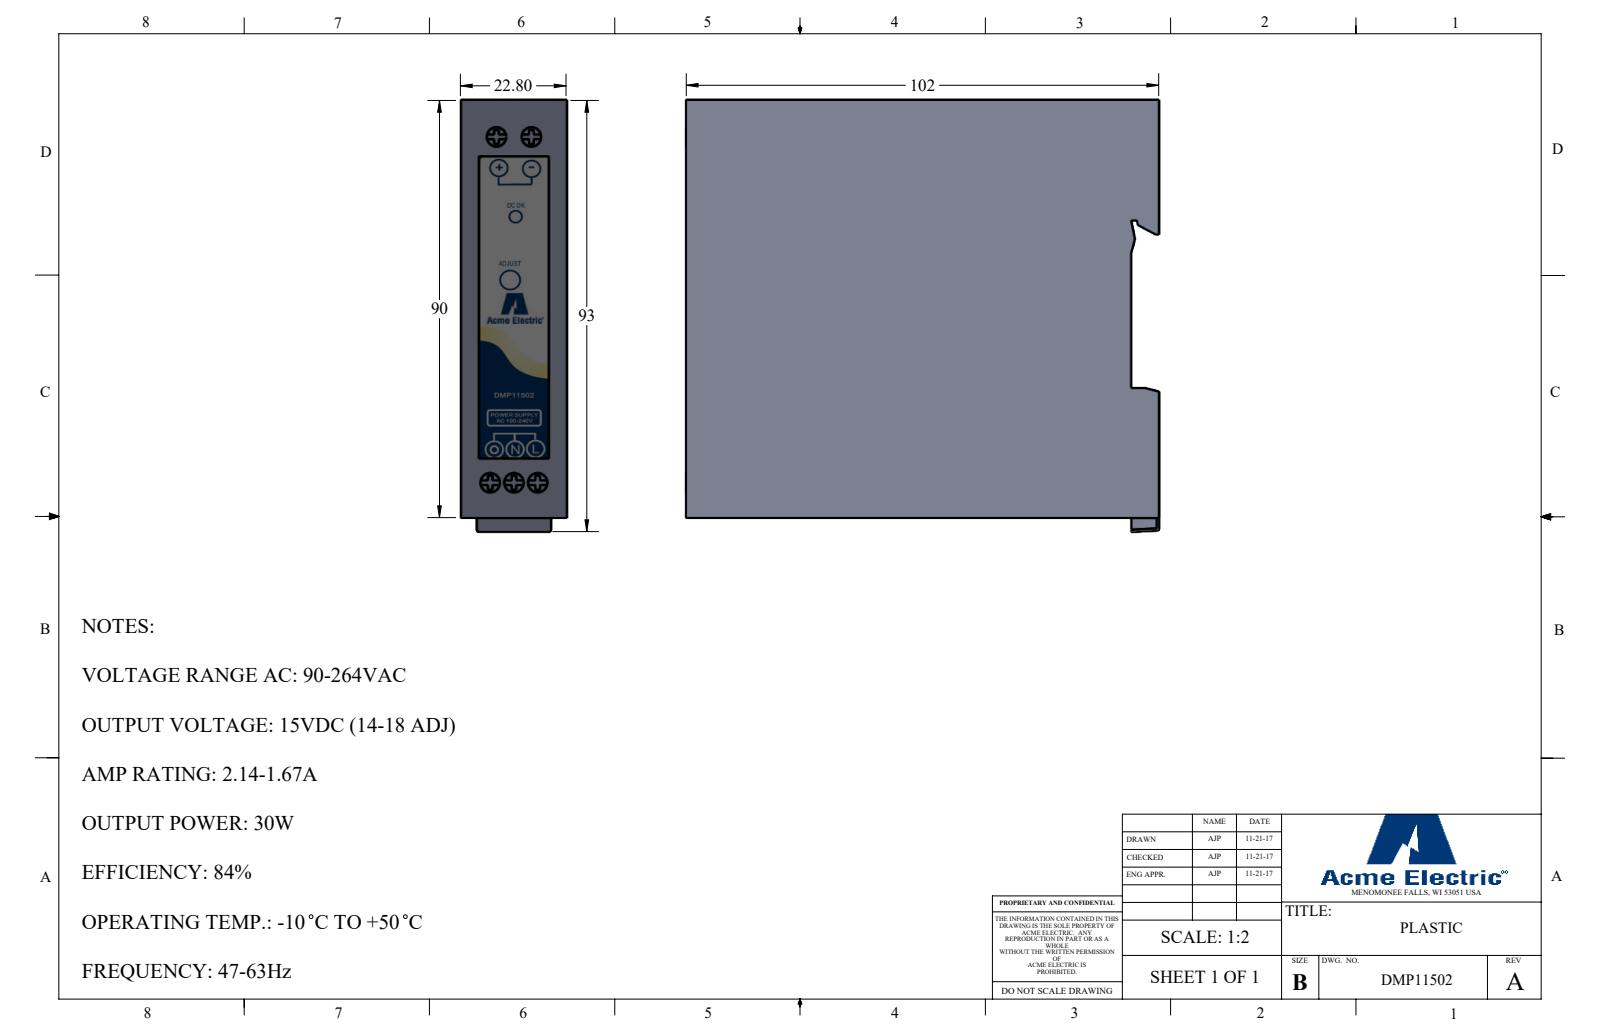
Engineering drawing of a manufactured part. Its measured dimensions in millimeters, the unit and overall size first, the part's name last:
Units: millimetres
Overall size (bounding box): 102 × 93 × 22.8
Round holes (diameter × count): ⌀4.2 ×5
Partial cylindrical surfaces — rounded edges, fillets, slot ends (radius × count): R0.5 ×5
Main face-to-face distances: 22.8, 90, 102, 6, 96, 28, 62, 1, 101, 95
Hole centre spacings: 5.1, 74.41, 74.49, 74.92, 7.5, 10.2
Volume: 204 839 mm³ · Surface area: 27 269 mm²
Bodies: 1 solid, 103 faces (86 planar, 15 cylindrical, 2 other)
Part name (STEP PRODUCT): DMP11502
STEP written by: SolidWorks 2017 (AUTOMOTIVE_DESIGN)
